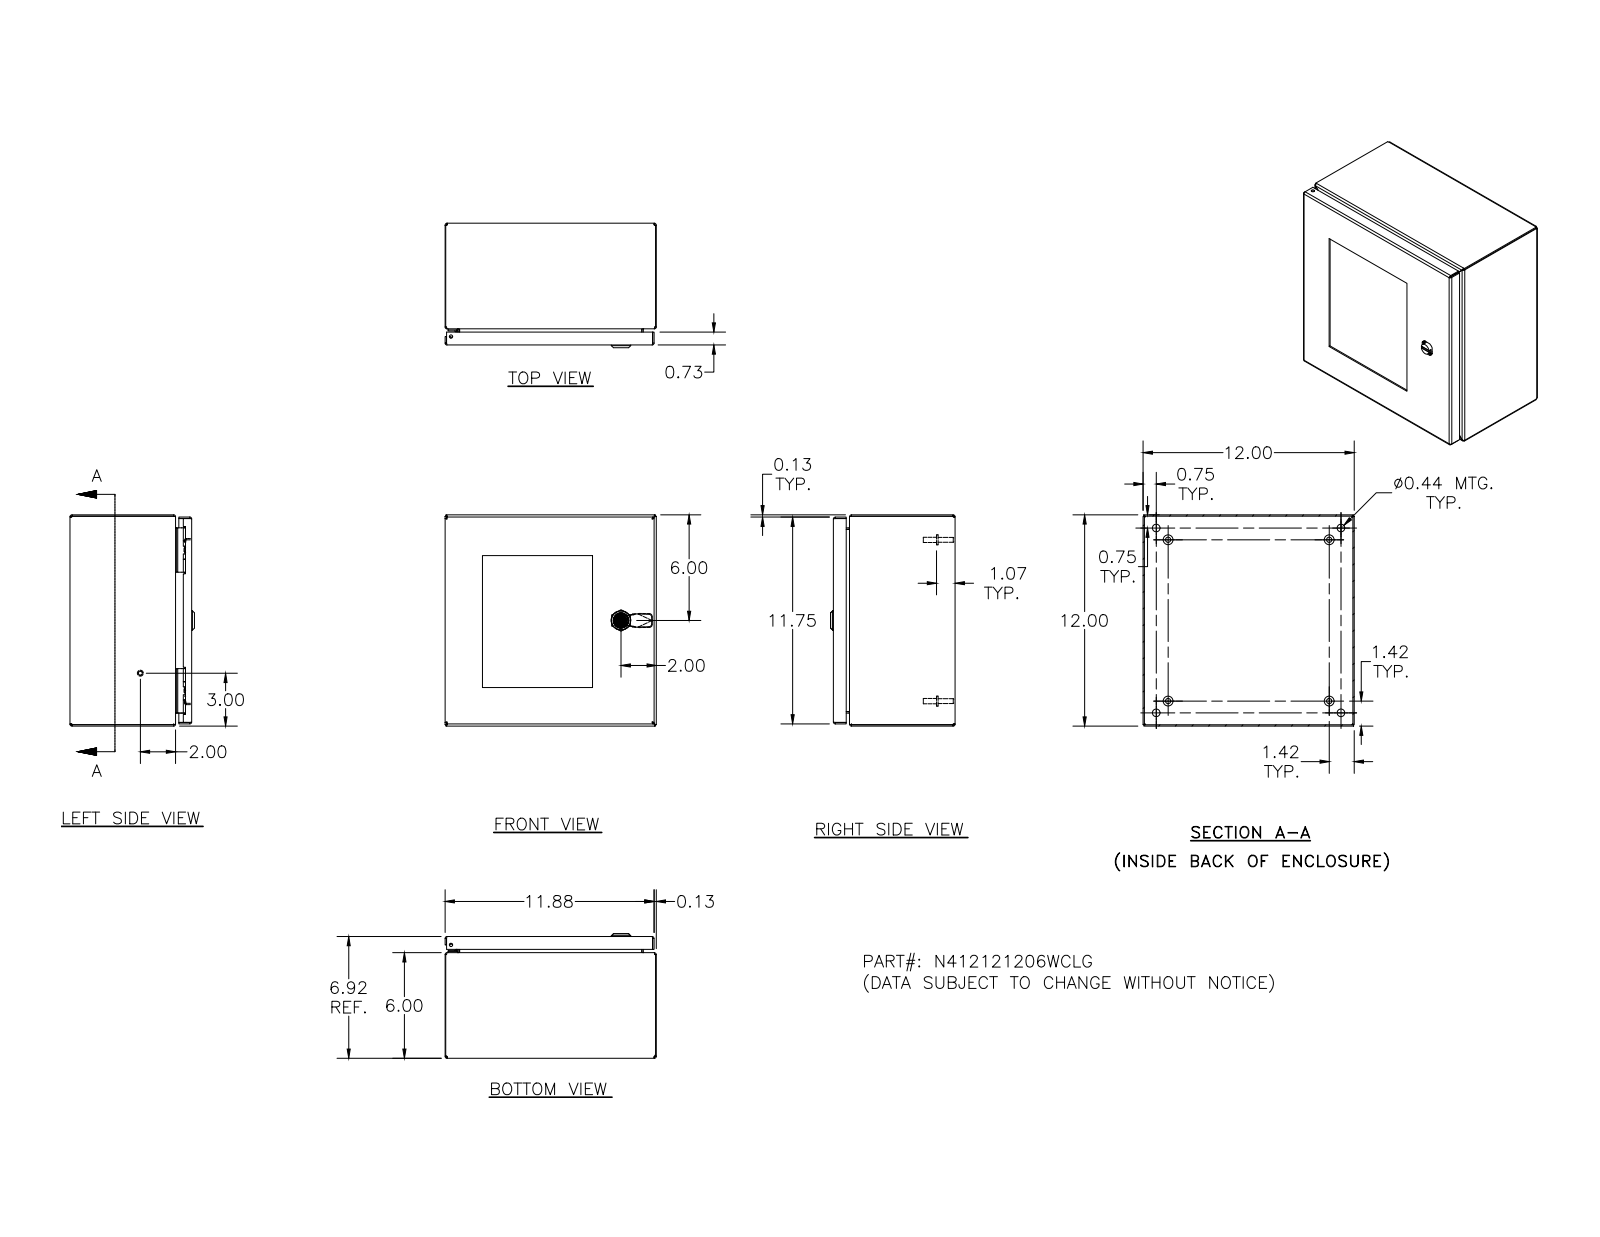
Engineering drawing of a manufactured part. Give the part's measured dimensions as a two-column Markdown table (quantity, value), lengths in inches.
| quantity | value |
| --- | --- |
| part name | N412121206WCLG |
| STEP written by | SolidWorks 2018 (AUTOMOTIVE_DESIGN) |
| units | inches |
| bodies | 53 solids, 1763 faces (665 planar, 585 cylindrical, 513 other) |
| overall size | 12 × 12 × 7.075 |
| volume | 65.18 in³ |
| surface area | 1 498 in² |
| round holes (diameter × count) | 0.156 × 10, 0.281 × 8, 0.188 × 5, 0.093 × 4, 0.152 × 4, 0.167 × 4, 0.172 × 4, 0.437 × 4, 0.187 × 1, 0.197 × 1, 0.315 × 1, 0.394 × 1 |
| round bosses / shafts (diameter × count) | 0.25 × 10, 0.337 × 8, 0.19 × 8, 0.563 × 4, 0.36 × 4, 0.32 × 4, 0.3 × 4, 0.275 × 4 |
| partial cylindrical surfaces (radius × count) | 0.031 × 34, 0.012 × 30, 0.05 × 26, 0.105 × 24, 0.016 × 18, 0.125 × 16, 0.02 × 13, 0.032 × 8 |
| main face-to-face distances | 0.074, 11.926, 6.843, 6.769, 11.852, 12, 6.917, 0.25, 6.593, 6.519 |
| hole center spacings | 8, 4, 6.221, 8.585, 10.5, 8.927, 0.5, 0.656 |
